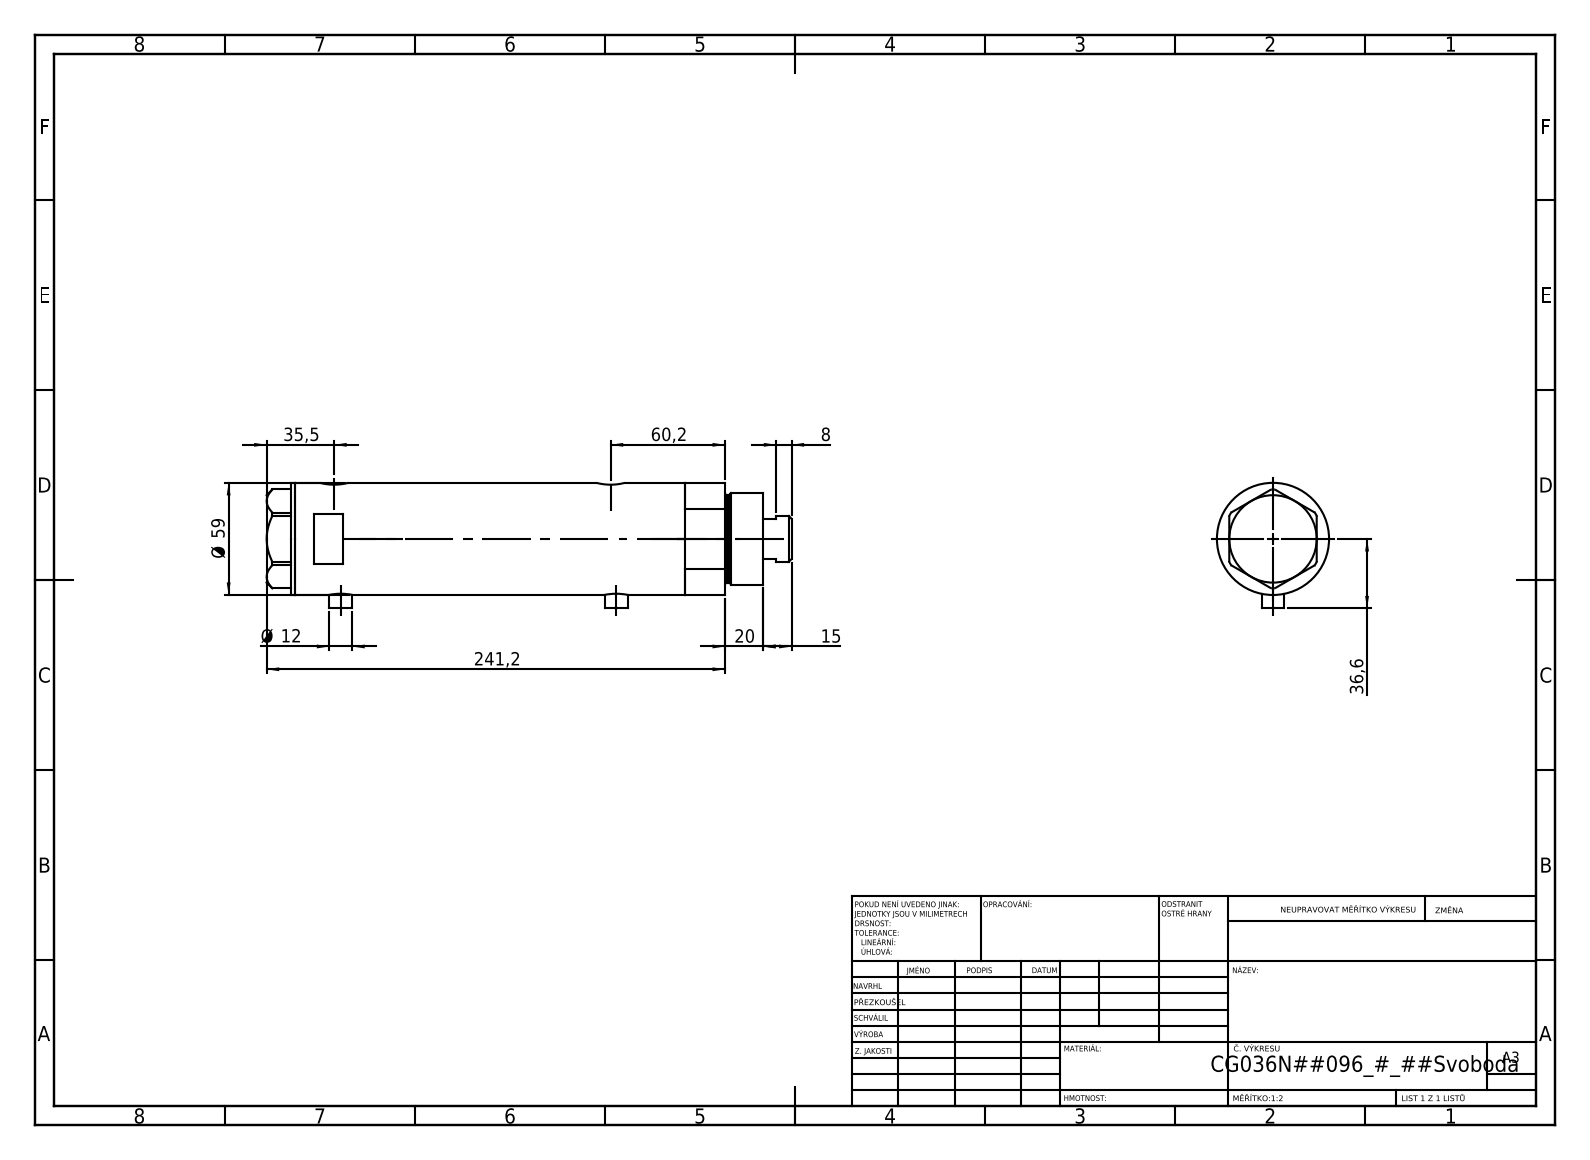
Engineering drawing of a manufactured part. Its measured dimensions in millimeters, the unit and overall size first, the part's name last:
Units: millimetres
Overall size (bounding box): 276.2 × 66.1 × 59
Round holes (diameter × count): ⌀5 ×2, ⌀9.73 ×2, ⌀12.5 ×2, ⌀15 ×2, ⌀8.5 ×1, ⌀25 ×1, ⌀26.5 ×1, ⌀36 ×1, ⌀40 ×1, ⌀52 ×1
Round bosses / shafts (diameter × count): ⌀12 ×2, ⌀59 ×1, ⌀48 ×1, ⌀46 ×1, ⌀24 ×1
Main face-to-face distances: 167.2, 23.5, 143.7, 15, 38.5, 182.2, 2, 261.2, 246.2, 222.7
Hole centre spacings: 2.9, 3.5, 142, 144.9, 145.5, 148.4
Volume: 631 333 mm³ · Surface area: 125 498 mm²
Bodies: 4 solids, 126 faces (53 planar, 53 cylindrical, 20 other)
Part name (STEP PRODUCT): V270CG_VC; V270CG_FRONT; V270CG_MIDDLE; V270CG_BACK
STEP written by: SolidWorks 2019 (CONFIG_CONTROL_DESIGN)
